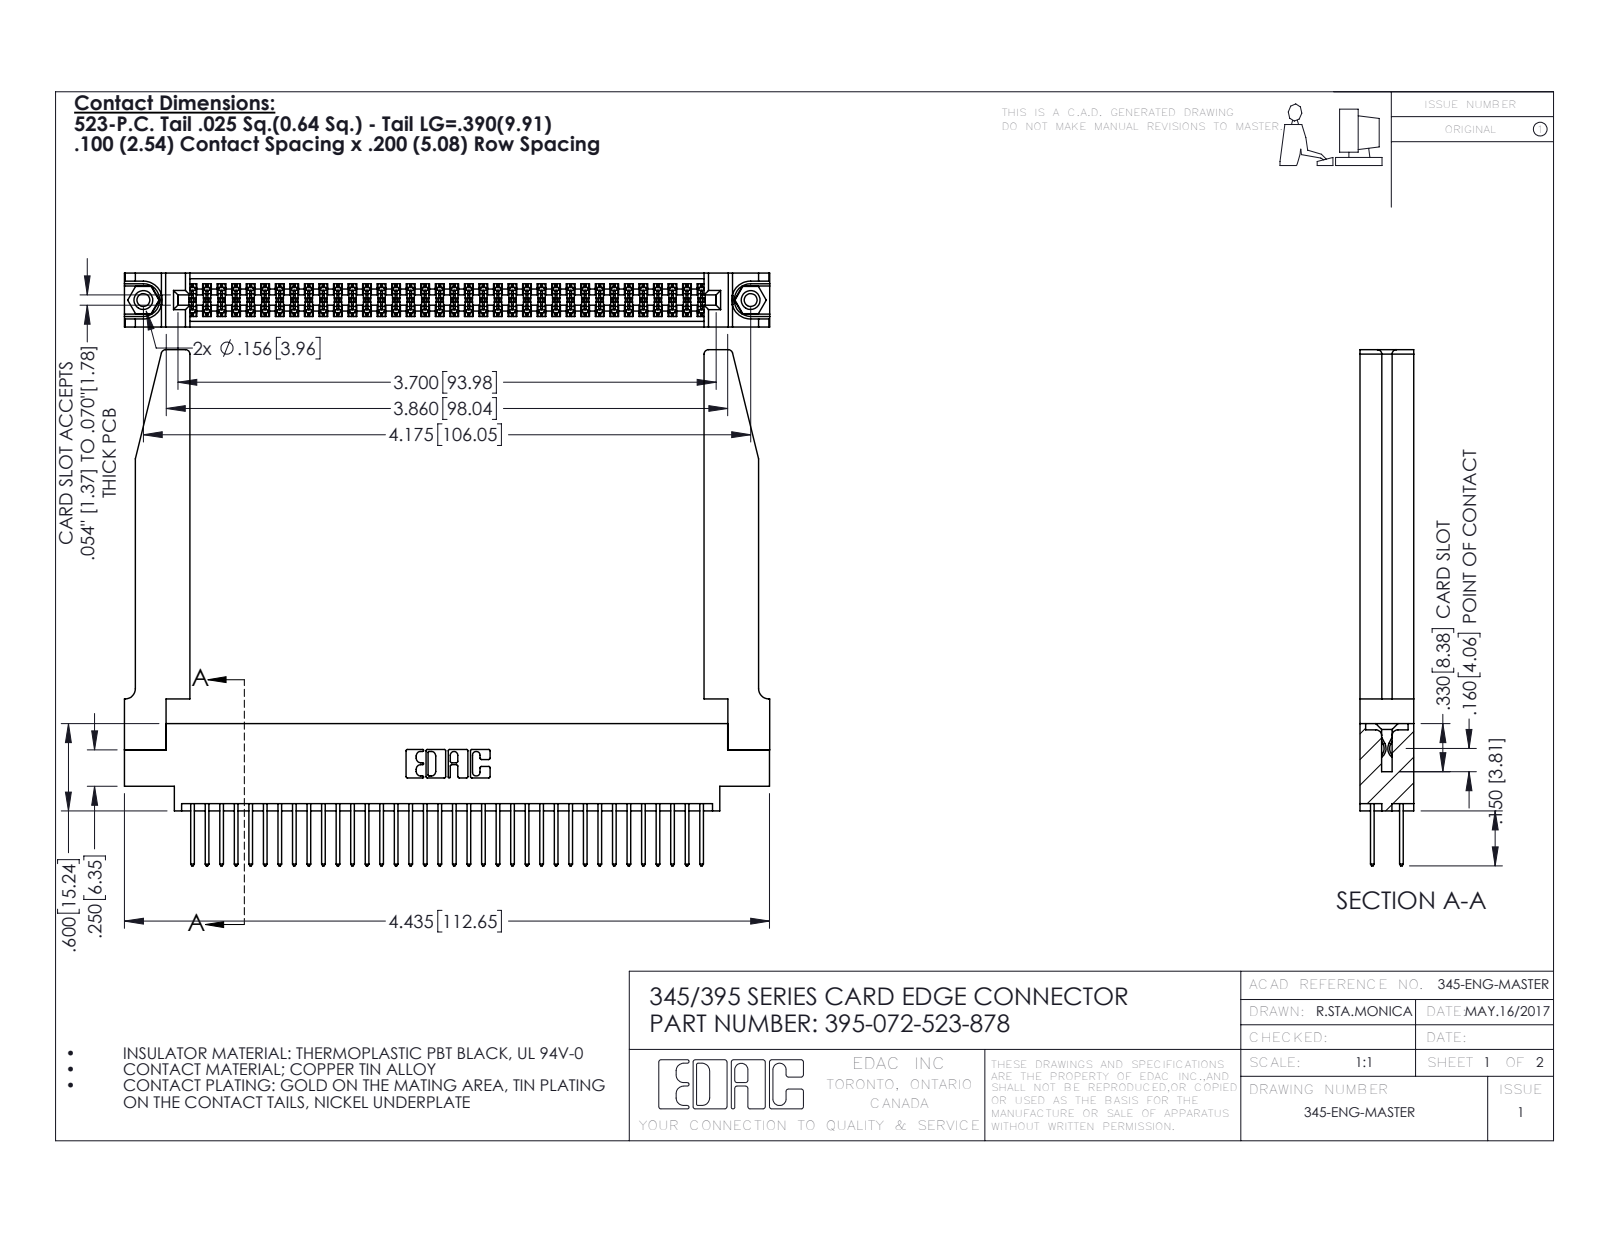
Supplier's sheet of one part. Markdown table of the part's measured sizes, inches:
| quantity | value |
| --- | --- |
| part name | 395-072-523-878; 345-250-001_345-250-001-102; 345 Part_0.170 Offset - 0.156 Dia-TH; 345-292-001_345-293-123 (+1 more) |
| STEP written by | SolidWorks 2016 (CONFIG_CONTROL_DESIGN) |
| units | inches |
| bodies | 77 solids, 3964 faces (2602 planar, 1310 cylindrical, 52 other) |
| overall size | 4.436 × 3.547 × 0.37 |
| volume | 1.141 in³ |
| surface area | 36.7 in² |
| round holes (diameter × count) | 0.089 × 2, 0.125 × 2, 0.156 × 2, 0.064 × 1 |
| round bosses / shafts (diameter × count) | 0.155 × 2 |
| partial cylindrical surfaces (radius × count) | 0.006 × 108, 0.01 × 72, 0.01 × 22, 0.03 × 8, 0.007 × 6, 0.031 × 6, 0.026 × 3, 0.014 × 2 |
| main face-to-face distances | 0.37, 0.072, 0.298, 0.2, 0.098, 0.272, 0.025, 0.225, 0.175, 0.148 |
| hole center spacings | 0.27, 3.939, 4.175 |
